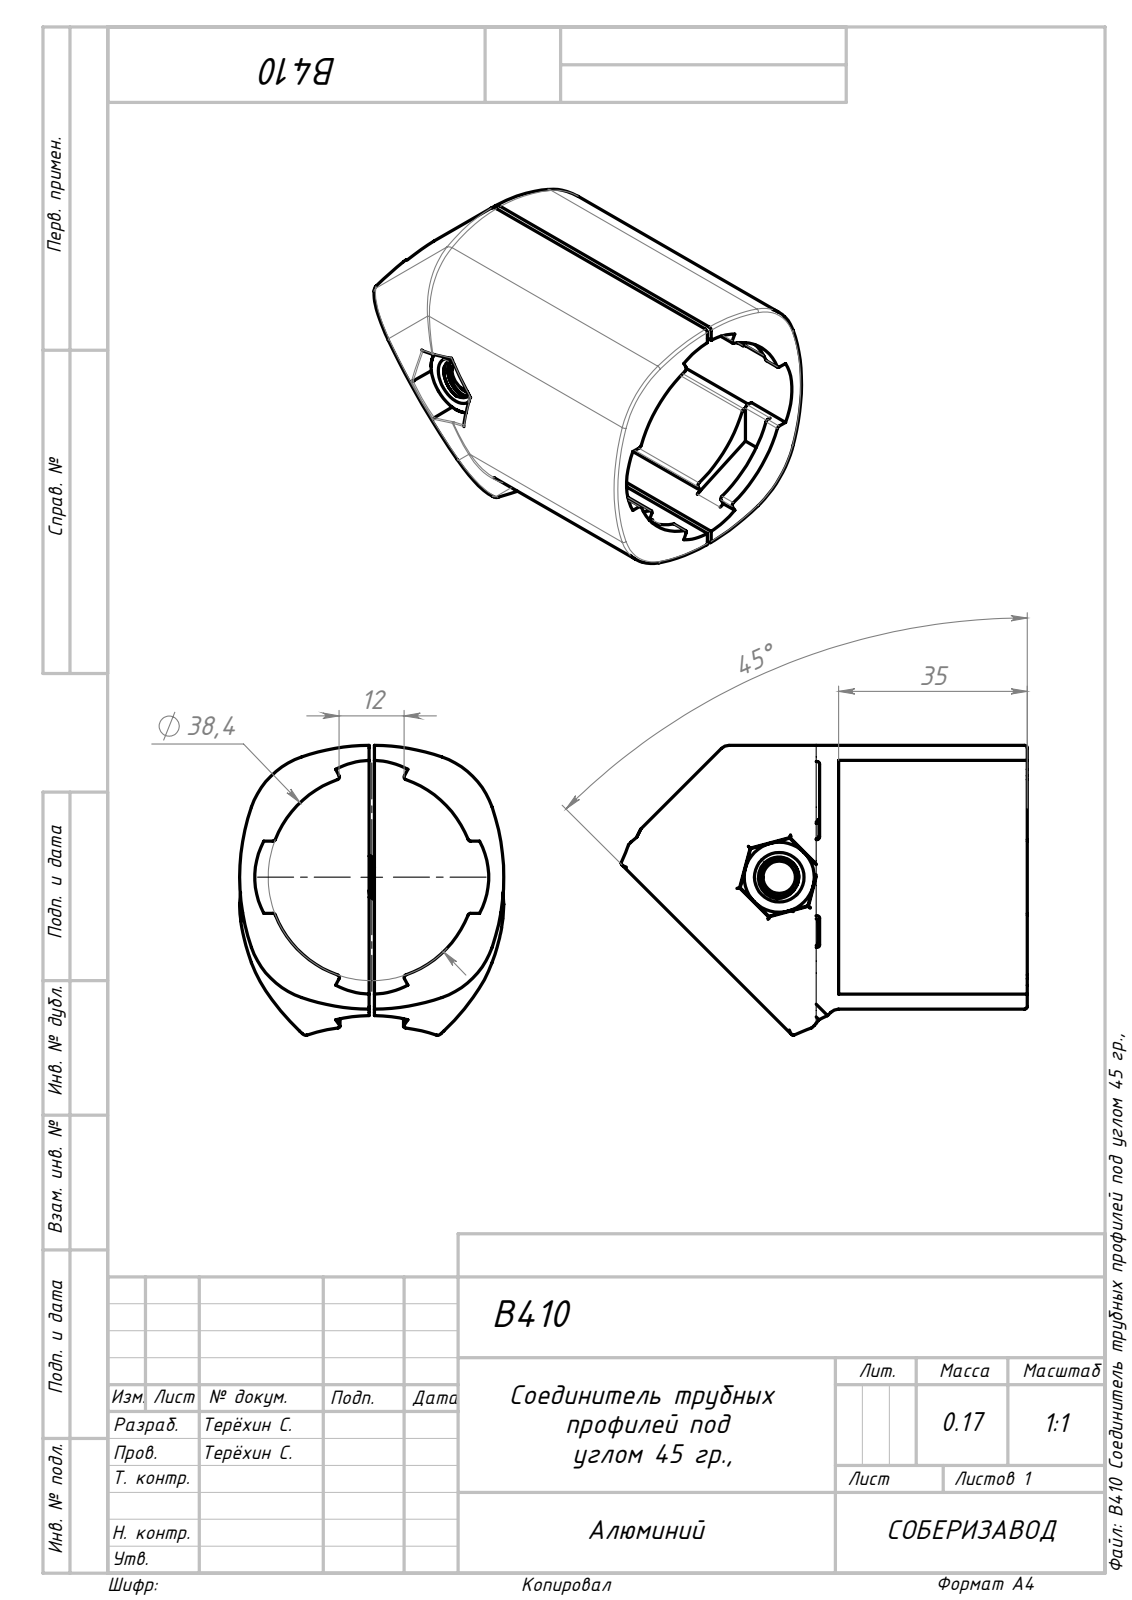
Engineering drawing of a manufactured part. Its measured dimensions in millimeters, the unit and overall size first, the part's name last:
Units: millimetres
Overall size (bounding box): 75.34 × 53.84 × 49
Round holes (diameter × count): ⌀7.2 ×1, ⌀8.5 ×1
Round bosses / shafts (diameter × count): ⌀12.3 ×1, ⌀8 ×1
Partial cylindrical surfaces — rounded edges, fillets, slot ends (radius × count): R0.5 ×30, R15 ×8, R40 ×8, R37 ×6, R14.2 ×5, R1 ×4, R12 ×4, R19 ×1
Main face-to-face distances: 1, 35, 12.81, 11, 19, 7, 12, 26, 8, 2.88
Volume: 62 071 mm³ · Surface area: 29 013 mm²
Bodies: 4 solids, 383 faces (98 planar, 155 cylindrical, 130 other)
Part name (STEP PRODUCT): B410 Соединитель трубных профилей под углом 45 гр.,
STEP written by: SolidWorks 2022 (AUTOMOTIVE_DESIGN)
